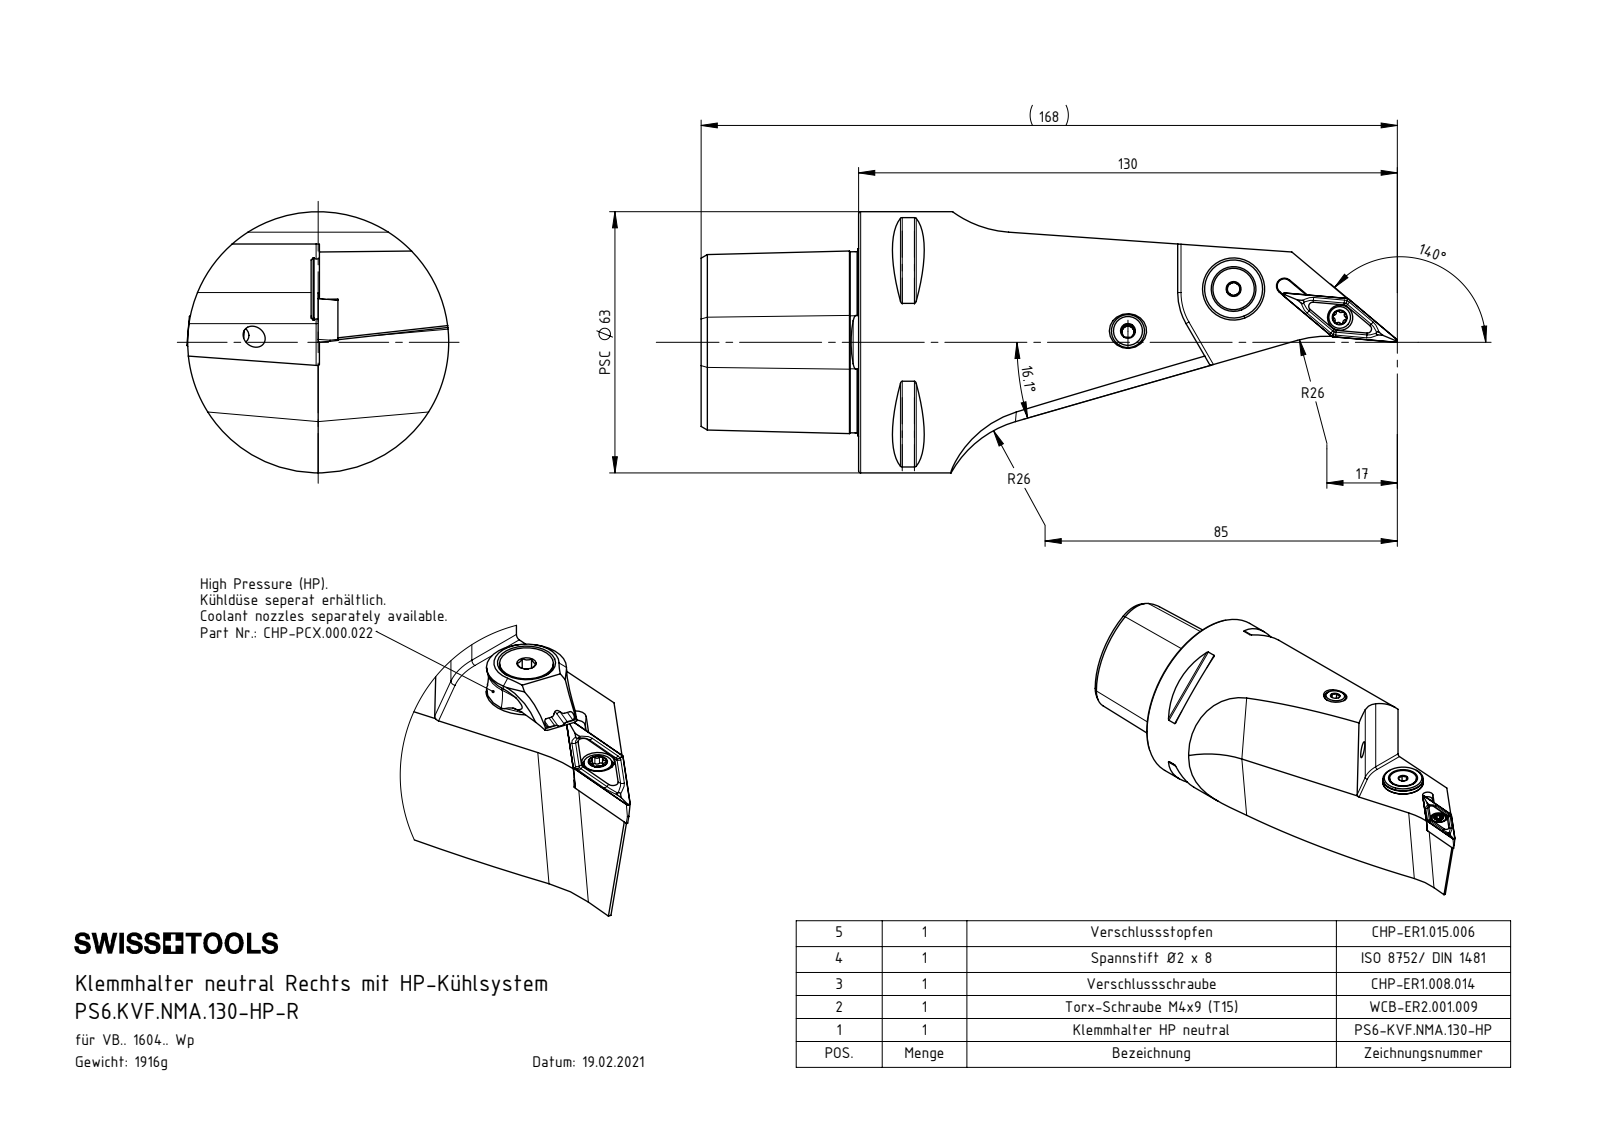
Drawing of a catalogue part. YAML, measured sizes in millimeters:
part_name: "VBMT160404; DIN 3771 - 13x1; 6-K.F.NMA.130-HP-R; PS6-KVF.NMA.130-HP-R_A (+6 more)"
step_written_by: "SolidWorks 2017 (AUTOMOTIVE_DESIGN)"
units: millimeters
bodies: {solids: 8, faces: 275, planar: 92, cylindrical: 66, other: 117}
overall_size: [168, 63.19, 63]
volume: 244003
surface_area: 39202
round_holes:
  - {diameter: 4.2, count: 2}
  - {diameter: 5, count: 2}
  - {diameter: 1.2, count: 1}
  - {diameter: 2, count: 1}
  - {diameter: 2.5, count: 1}
  - {diameter: 3, count: 1}
  - {diameter: 3.3, count: 1}
  - {diameter: 4, count: 1}
  - {diameter: 4.4, count: 1}
  - {diameter: 5.2, count: 1}
  - {diameter: 6.1, count: 1}
  - {diameter: 7, count: 1}
round_bosses_or_shafts:
  - {diameter: 63, count: 1}
  - {diameter: 15, count: 1}
  - {diameter: 13.4, count: 1}
  - {diameter: 10, count: 1}
  - {diameter: 8, count: 1}
  - {diameter: 5.5, count: 1}
  - {diameter: 5.25, count: 1}
  - {diameter: 5, count: 1}
partial_cylinders:
  - {radius: 0.5, count: 8}
  - {radius: 0.34, count: 6}
  - {radius: 0.59, count: 6}
  - {radius: 26, count: 4}
  - {radius: 0.15, count: 2}
  - {radius: 0.8, count: 2}
  - {radius: 1.75, count: 1}
  - {radius: 6, count: 1}
face_to_face_distances: [38, 24.88, 115, 77, 4.46, 4.5, 27, 11, 88, 55.8]
hole_center_spacings: [4.5, 23.02, 23.14, 26.5, 26.62, 27.5, 79.54, 83.95]
